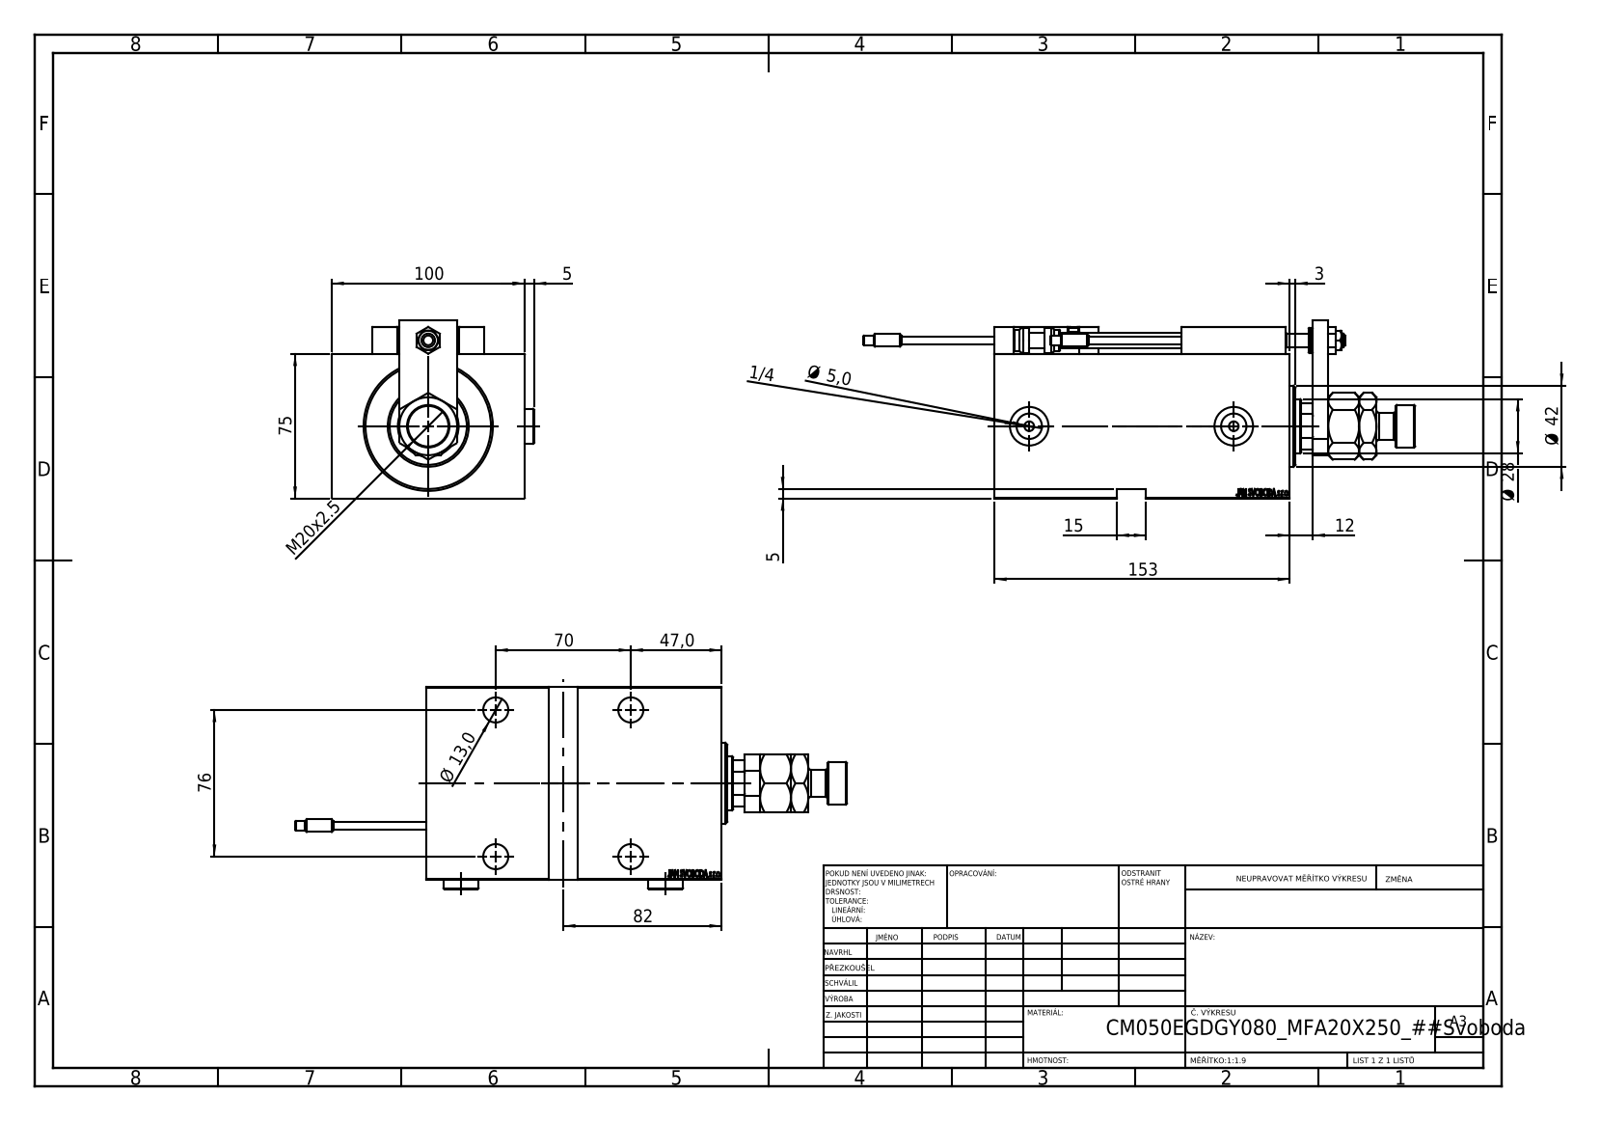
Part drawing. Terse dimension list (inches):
name: V450CM_E_VCP; Block; MAGNET; KONCOVKA_Y (+7 more)
written by: SolidWorks 2019 (CONFIG_CONTROL_DESIGN)
unit: in
bodies: 27 solids, 1423 faces (624 planar, 210 cylindrical, 589 other)
size: 11.26 × 4.13 × 3.642
volume: 65.11 in³; area: 272.2 in²
holes: 5× ⌀0.315, 4× ⌀0.126, 4× ⌀0.157, 4× ⌀0.197, 4× ⌀0.512, 4× ⌀0.748, 3× ⌀0.787, 2× ⌀0.518, 1× ⌀0.276, 1× ⌀0.728, 1× ⌀1.102, 1× ⌀1.24
bosses: 4× ⌀0.197, 2× ⌀0.709, 2× ⌀0.256, 2× ⌀0.15, 1× ⌀2.047, 1× ⌀1.654, 1× ⌀0.866, 1× ⌀0.551
rounds: 30× R0.012, 2× R0.118, 1× R0.531
face distances: 2.953, 3.937, 0.551, 6.024, 0.197, 5.472, 0.984, 0.787, 0.315, 0.472
hole spacings: 0.448, 0.787, 1.165, 1.169, 1.42, 1.644, 1.661, 1.922
